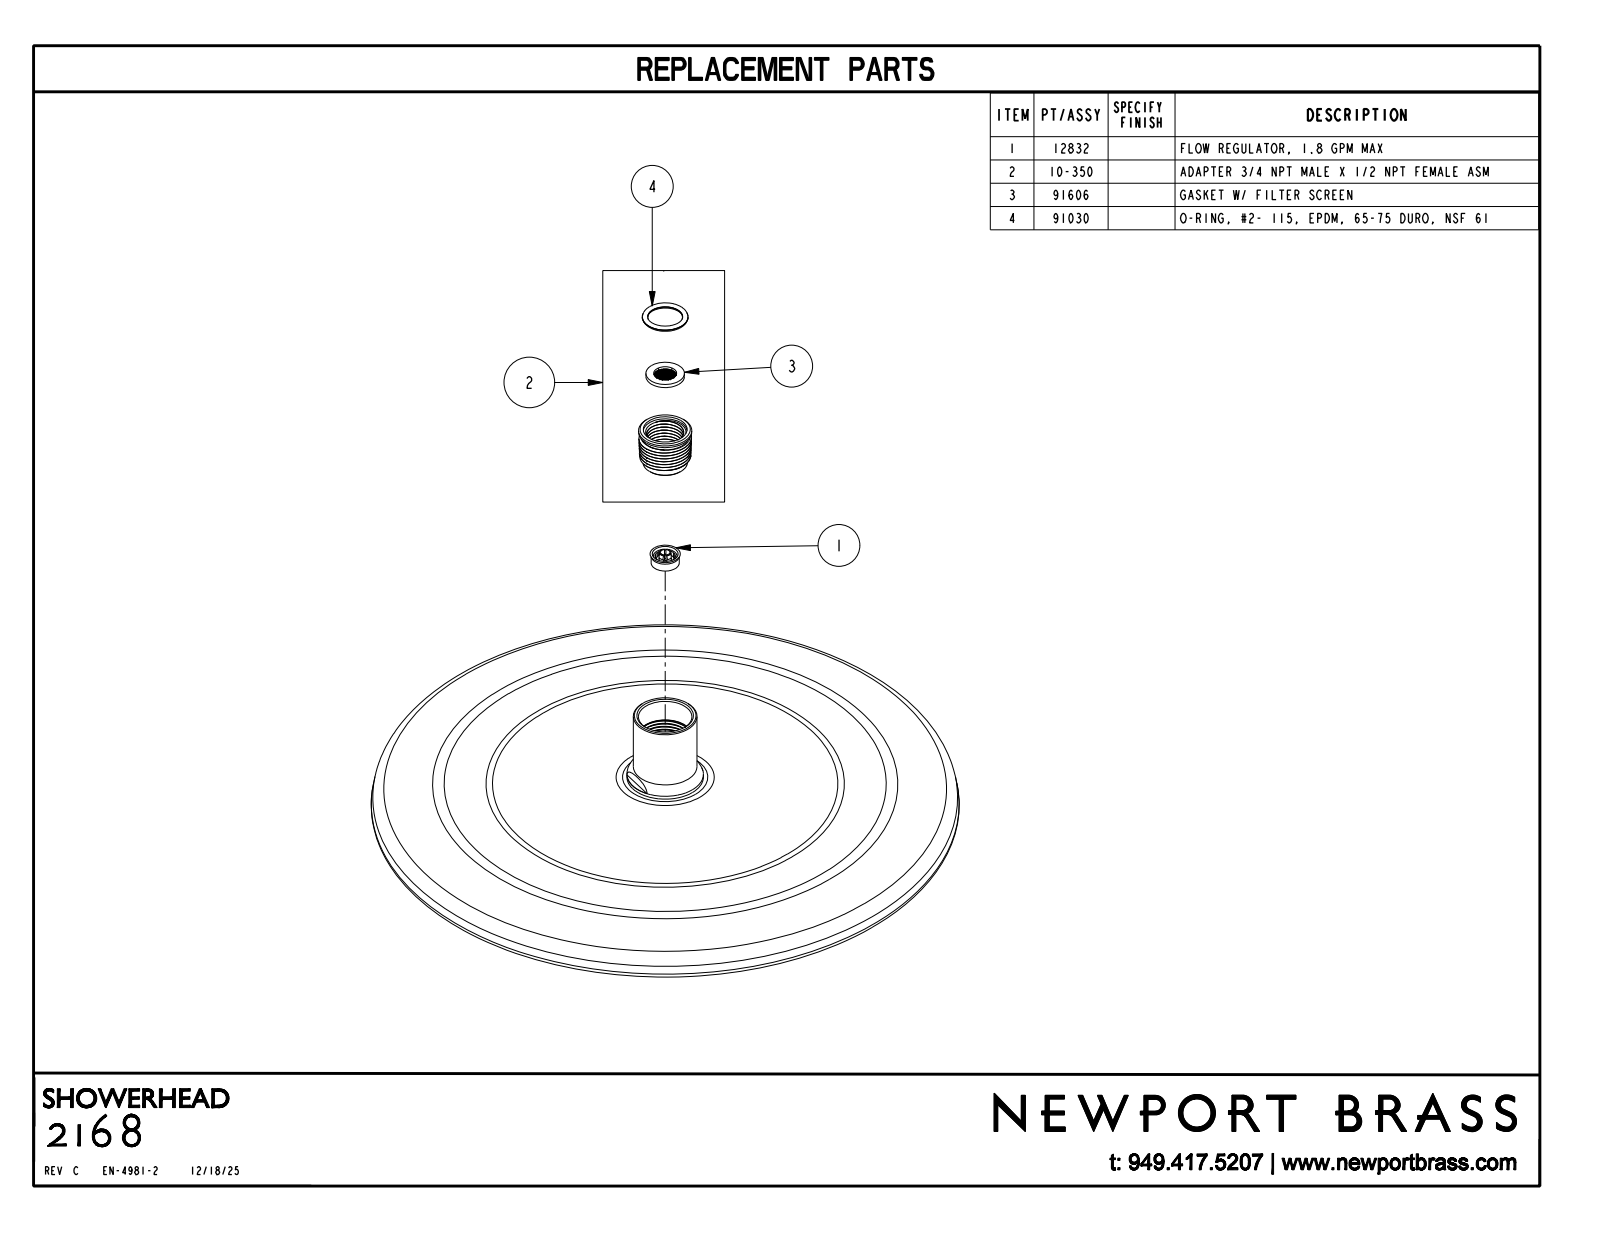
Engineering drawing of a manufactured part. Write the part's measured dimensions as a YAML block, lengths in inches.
part_name: "2168"
step_written_by: "CREO PARAMETRIC BY PTC INC, 2023134 (CONFIG_CONTROL_DESIGN)"
units: inches
bodies: {solids: 1, faces: 2573, planar: 743, cylindrical: 1084, other: 746}
overall_size: [11.55, 11.55, 2.327]
volume: 65.72
surface_area: 235.5
round_holes:
  - {diameter: 0.087, count: 180}
  - {diameter: 0.16, count: 180}
round_bosses_or_shafts:
  - {diameter: 0.142, count: 180}
  - {diameter: 1.502, count: 1}
  - {diameter: 1.25, count: 1}
face_to_face_distances: [0.622, 0.611, 2.262, 2.252, 1.641, 0.049, 0.059, 0.671, 2.311, 0.016]
hole_center_spacings: [0.578, 0.579, 0.579, 0.896, 1.099, 1.516, 1.782, 0.659]
